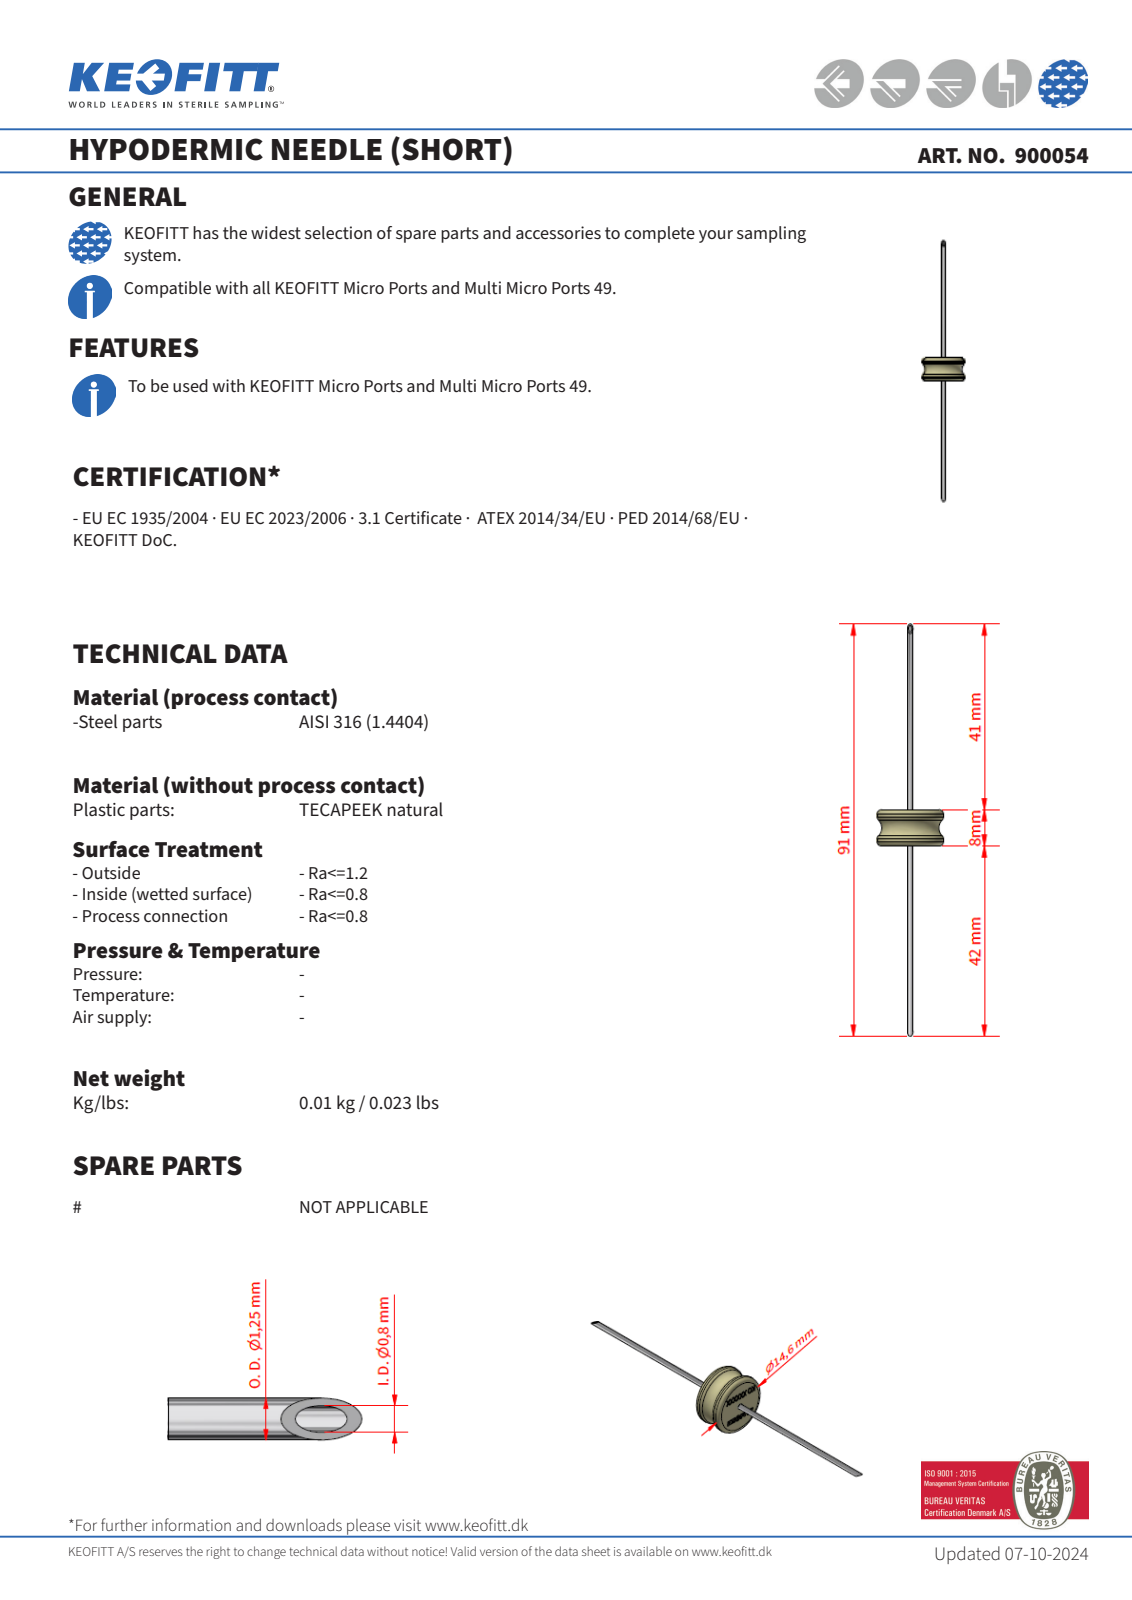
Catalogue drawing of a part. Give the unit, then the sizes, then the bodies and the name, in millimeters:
Units: millimetres
Overall size (bounding box): 91 × 14.6 × 14.6
Round holes (diameter × count): ⌀0.8 ×1, ⌀1.35 ×1
Round bosses / shafts (diameter × count): ⌀14.6 ×1, ⌀1.25 ×1
Main face-to-face distances: 8, 63.45
Volume: 1 253 mm³ · Surface area: 1 283 mm²
Bodies: 2 solids, 12 faces (4 planar, 5 cylindrical, 3 other)
Part name (STEP PRODUCT): 900054
STEP written by: Autodesk Inventor 2020 (AUTOMOTIVE_DESIGN)
